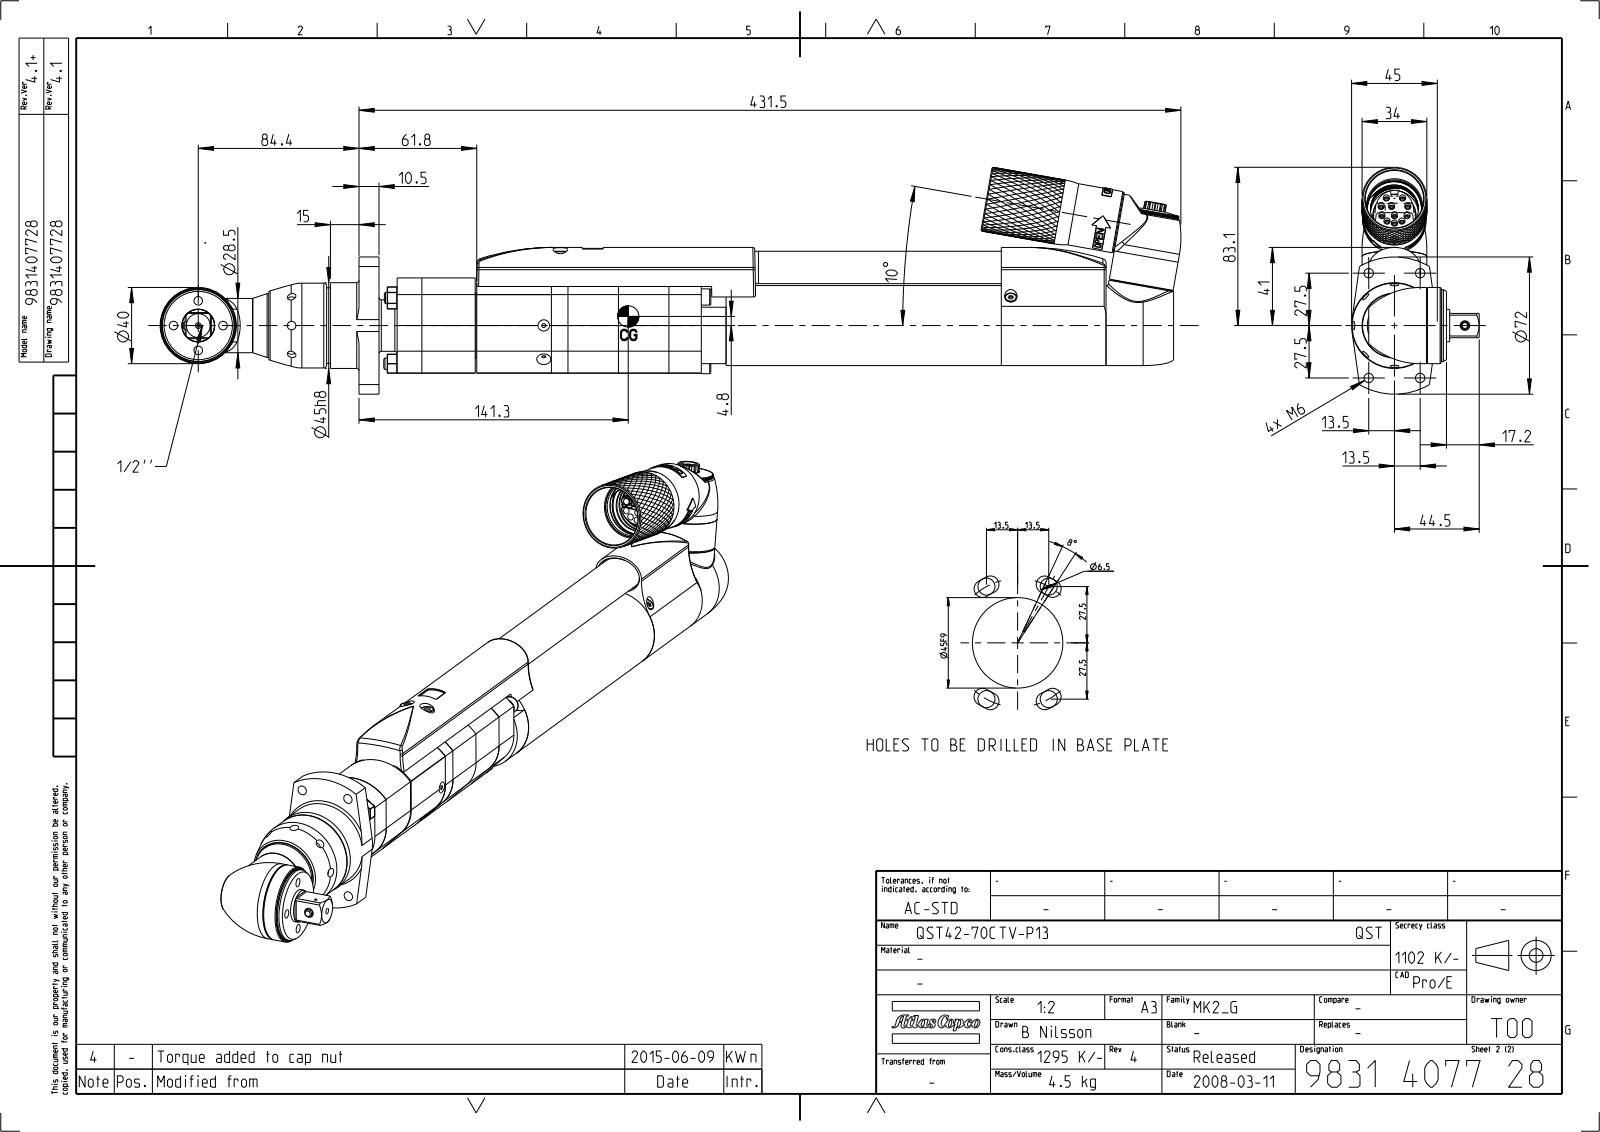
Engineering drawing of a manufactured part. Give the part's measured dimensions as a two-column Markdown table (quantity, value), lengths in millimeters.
| quantity | value |
| --- | --- |
| part name | 4230260102; 4230260112_ASM; 4230262500; 0219110017 (+8 more) |
| STEP written by | CREO PARAMETRIC BY PTC INC, 2015080 (CONFIG_CONTROL_DESIGN) |
| units | millimeters |
| bodies | 44 solids, 5058 faces (2089 planar, 1591 cylindrical, 1378 other) |
| overall size | 535.91 × 119.06 × 67 |
| volume | 489 240 mm³ |
| surface area | 292 270 mm² |
| round holes (diameter × count) | 2.64 × 11, 3.27 × 11, 3.6 × 11, 4.5 × 10, 3.3 × 7, 2.46 × 5, 3.24 × 5, 4.92 × 5, 1.4 × 3, 1.5 × 3, 2.94 × 3, 3.5 × 3 |
| round bosses / shafts (diameter × count) | 6 × 11, 3 × 7, 4 × 5, 34 × 4, 5 × 4, 8.5 × 3, 2.5 × 3, 30 × 2 |
| partial cylindrical surfaces (radius × count) | 1 × 79, 0.2 × 68, 0.1 × 53, 0.5 × 21, 0.29 × 12, 0.51 × 12, 2 × 9, 1.5 × 4 |
| main face-to-face distances | 38, 9.5, 3.5, 19, 13, 22.5, 26.5, 182.2, 159.7, 404.16 |
| hole center spacings | 7.16, 7.42, 15.92, 7.35, 15, 35, 7.41, 7.43 |
